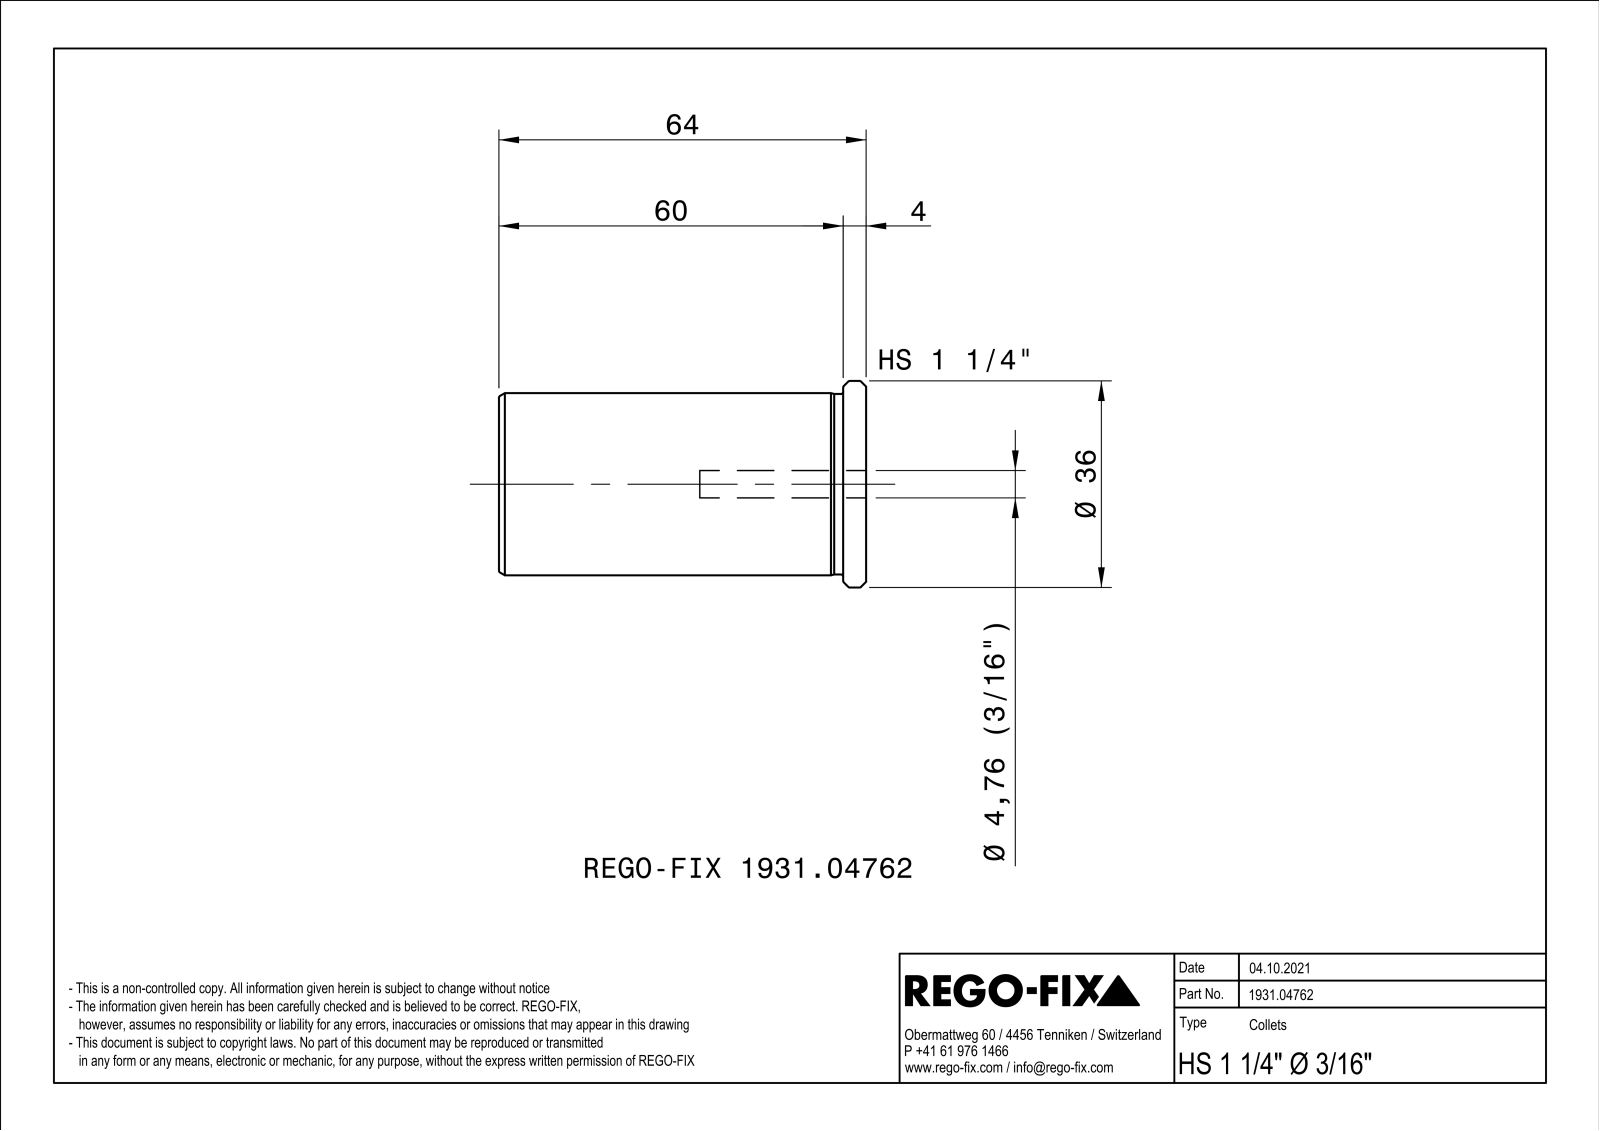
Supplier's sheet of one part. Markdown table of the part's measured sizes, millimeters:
| quantity | value |
| --- | --- |
| part name | NOCUT |
| STEP written by | SIEMENS PLM Software Solid Edge ST10 (AUTOMOTIVE_DESIGN) |
| units | millimeters |
| bodies | 1 solid, 72 faces (22 planar, 12 cylindrical, 38 other) |
| overall size | 64 × 35.99 × 35.99 |
| volume | 39 170 mm³ |
| surface area | 13 675 mm² |
| round holes (diameter × count) | 4.76 × 1, 10 × 1, 26.5 × 1 |
| round bosses / shafts (diameter × count) | 36 × 1, 31.75 × 1, 31.45 × 1 |
| main face-to-face distances | 1, 64, 4, 60 |
